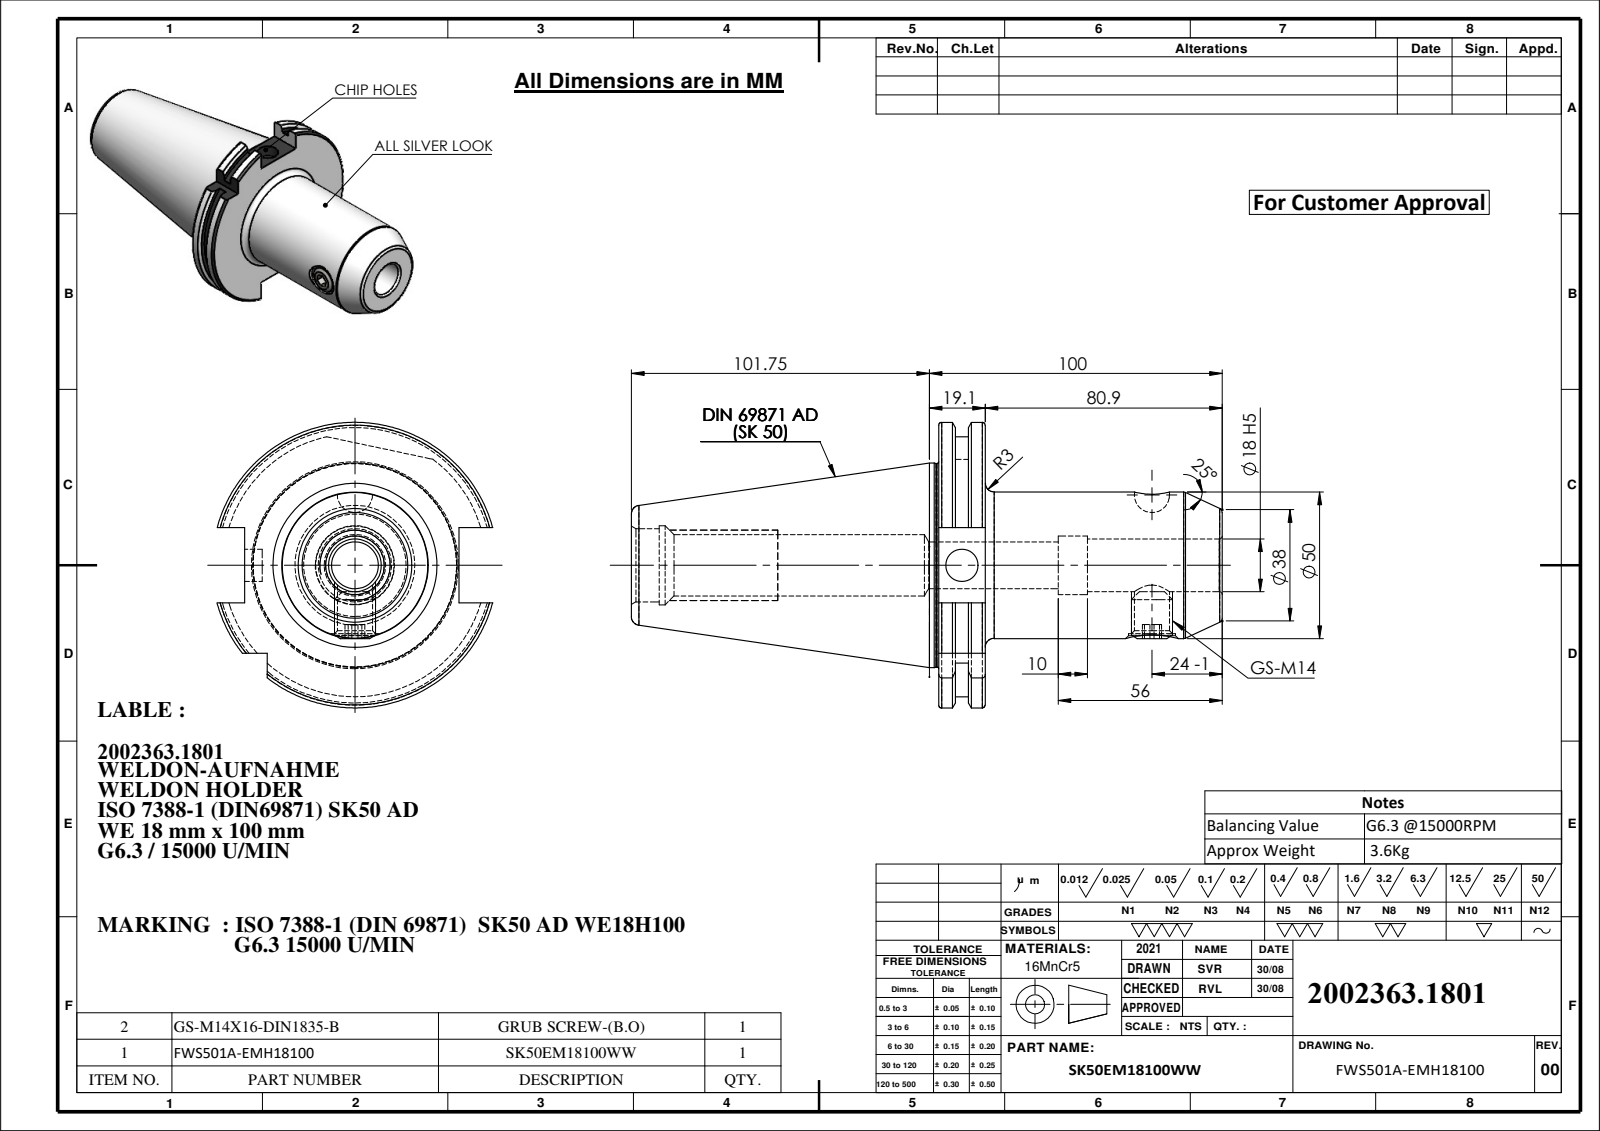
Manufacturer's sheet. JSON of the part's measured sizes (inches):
{"part_name": "FWS501A-EMH18100; SK50EM18100WW; M14X16_ISO 4026 - M12 x 12-N", "step_written_by": "SolidWorks 2024 (CONFIG_CONTROL_DESIGN)", "units": "inches", "bodies": {"solids": 2, "faces": 124, "planar": 33, "cylindrical": 39, "other": 52}, "overall_size": [7.943, 3.839, 3.703], "volume_in3": 27.76, "surface_area_in2": 95.33, "round_holes": [[0.63, 2], [0.433, 1], [0.472, 1], [0.709, 1], [0.787, 1], [0.827, 1], [0.984, 1], [1.063, 1]], "round_bosses_or_shafts": [[2.75, 1], [2.734, 1], [1.969, 1], [0.551, 1]], "partial_cylinders_radius": [[1.768, 1], [1.919, 1]], "face_to_face_distances": [0.626, 3.811, 3.185, 0.223, 0.403, 3.588, 0.4, 0.177, 0.226, 3.411]}
